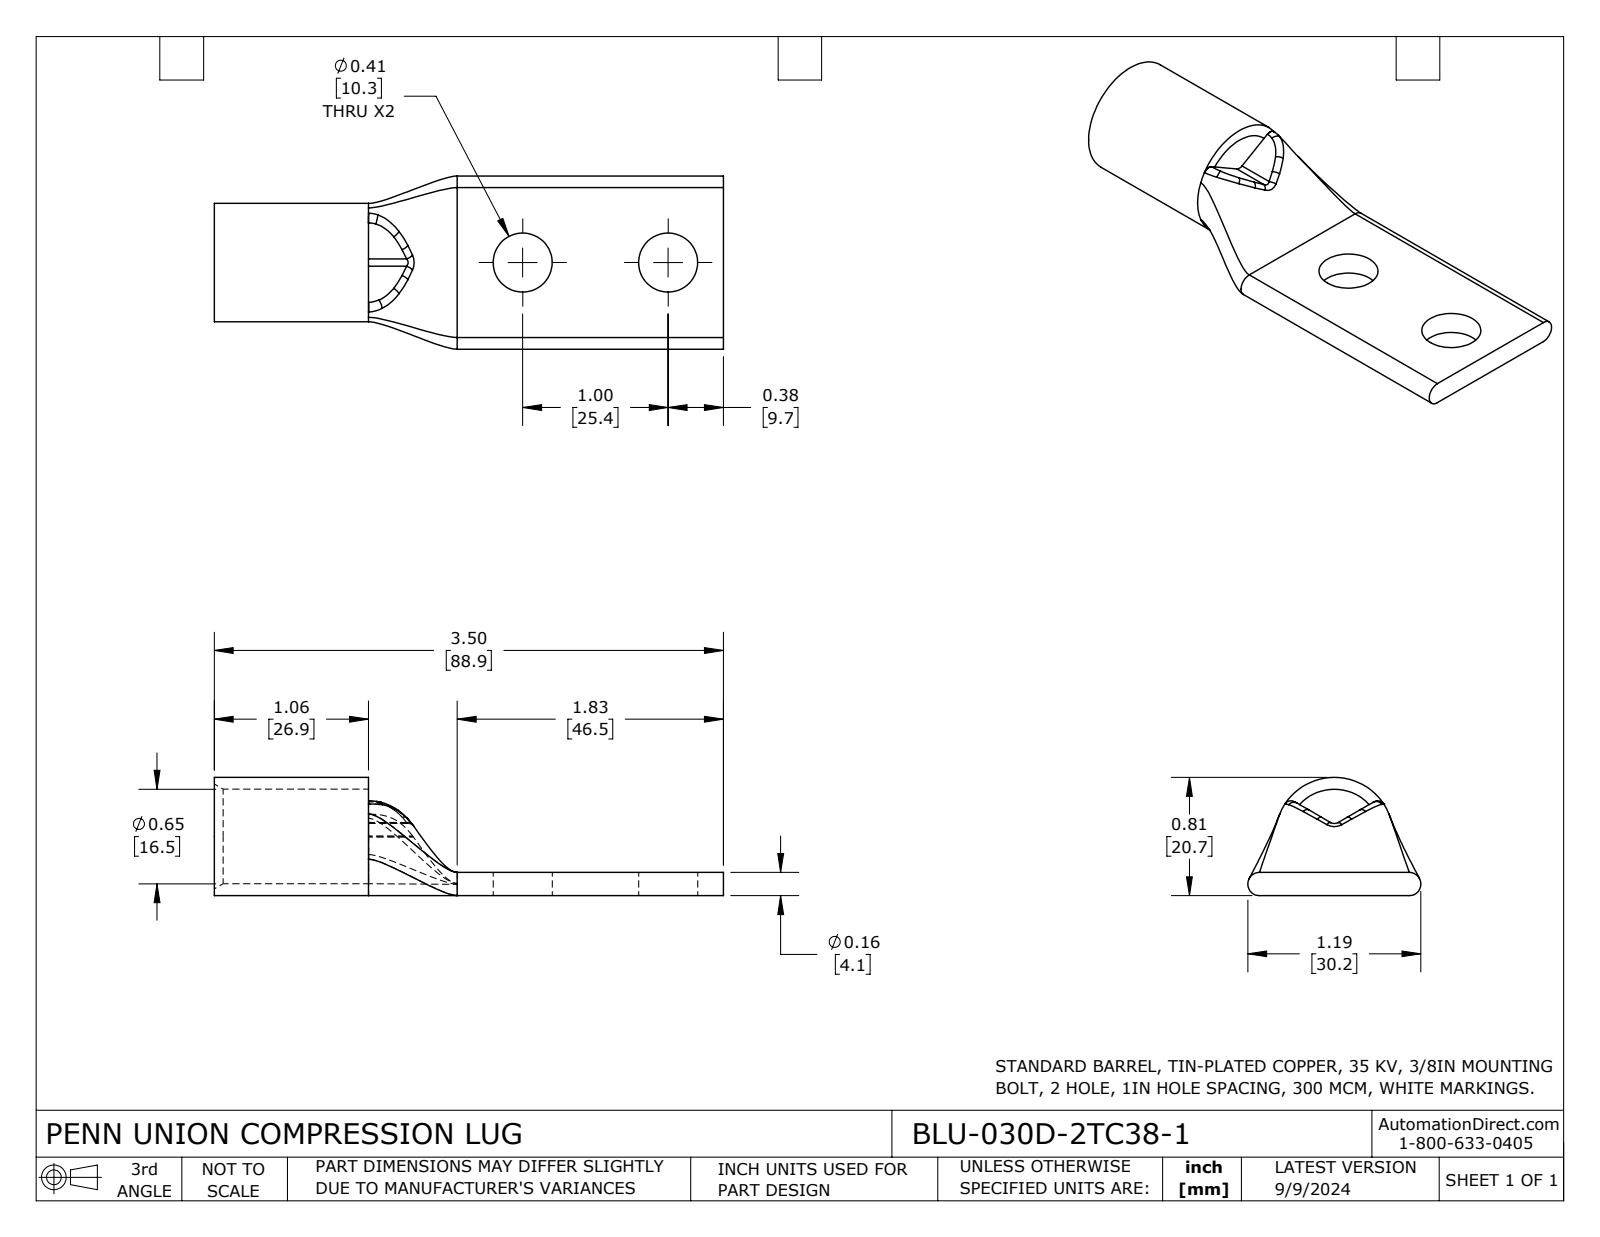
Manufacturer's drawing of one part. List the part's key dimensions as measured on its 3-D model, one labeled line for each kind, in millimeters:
Part name (STEP PRODUCT): BLU-030D-2TC38-1
STEP written by: SolidWorks 2023 (CONFIG_CONTROL_DESIGN)
Units: millimetres
Bodies: 1 solid, 45 faces (11 planar, 13 cylindrical, 21 other)
Overall size (bounding box): 88.9 × 30.2 × 20.7
Volume: 9 830 mm³ · Surface area: 8 361 mm²
Round holes (diameter × count): ⌀10.3 ×2, ⌀16.5 ×1
Round bosses / shafts (diameter × count): ⌀20.7 ×1
Partial cylindrical surfaces — rounded edges, fillets, slot ends (radius × count): R1.3 ×2, R2 ×2
Main face-to-face distances: 4.1, 88.9, 2.1, 26.9, 62, 42.4, 15.5, 46.5
Hole centre spacings: 25.4
